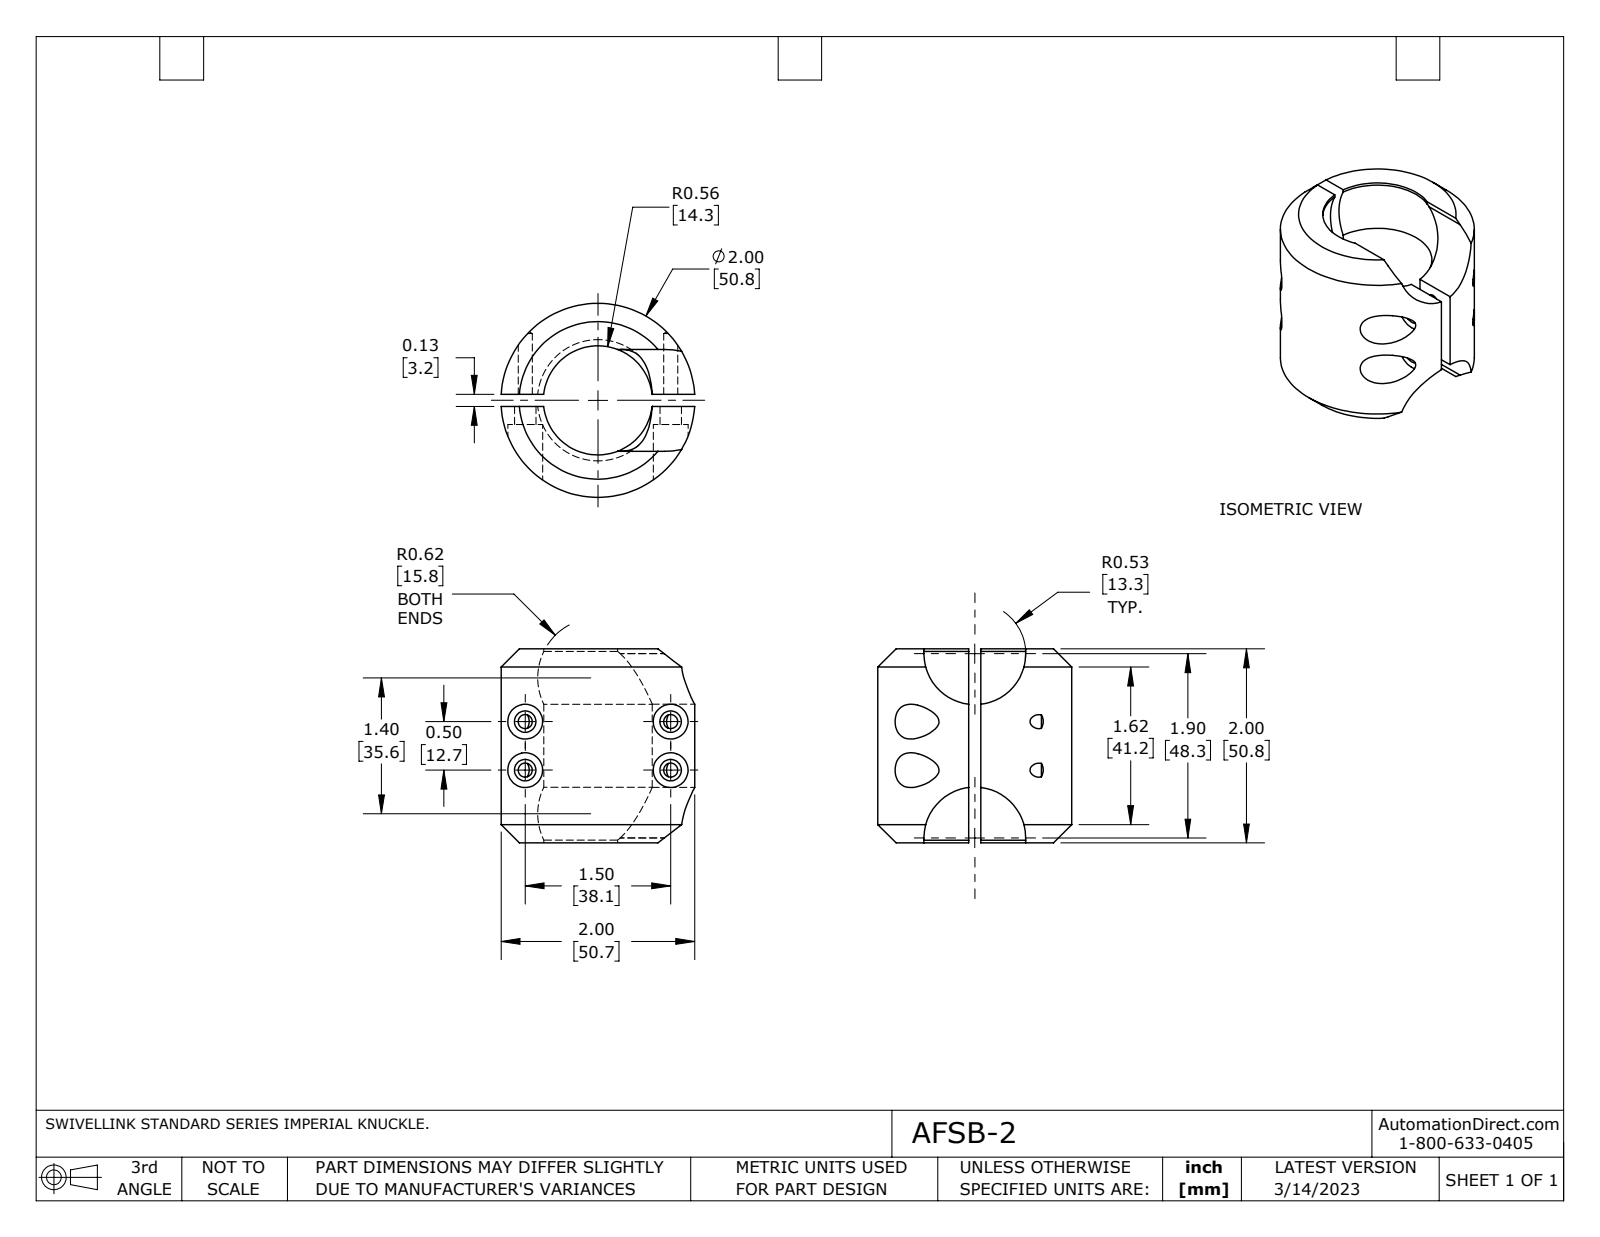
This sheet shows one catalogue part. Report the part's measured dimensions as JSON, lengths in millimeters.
{"part_name": "AFSB-2", "step_written_by": "SolidWorks 2021 (AUTOMOTIVE_DESIGN)", "units": "millimeters", "bodies": {"solids": 2, "faces": 52, "planar": 16, "cylindrical": 24, "other": 12}, "overall_size": [50.8, 50.8, 50.7], "volume_mm3": 51900, "surface_area_mm2": 16500, "round_holes": [[3.7, 4], [5.6, 4], [9.1, 4], [28.6, 1]], "round_bosses_or_shafts": [[50.8, 1]], "partial_cylinders_radius": [[13.3, 2]], "face_to_face_distances": [3.2, 50.8, 8, 4.7, 11.7, 14.9, 19.7, 26.7, 7], "hole_center_spacings": [12.7, 38.1, 40.2]}
